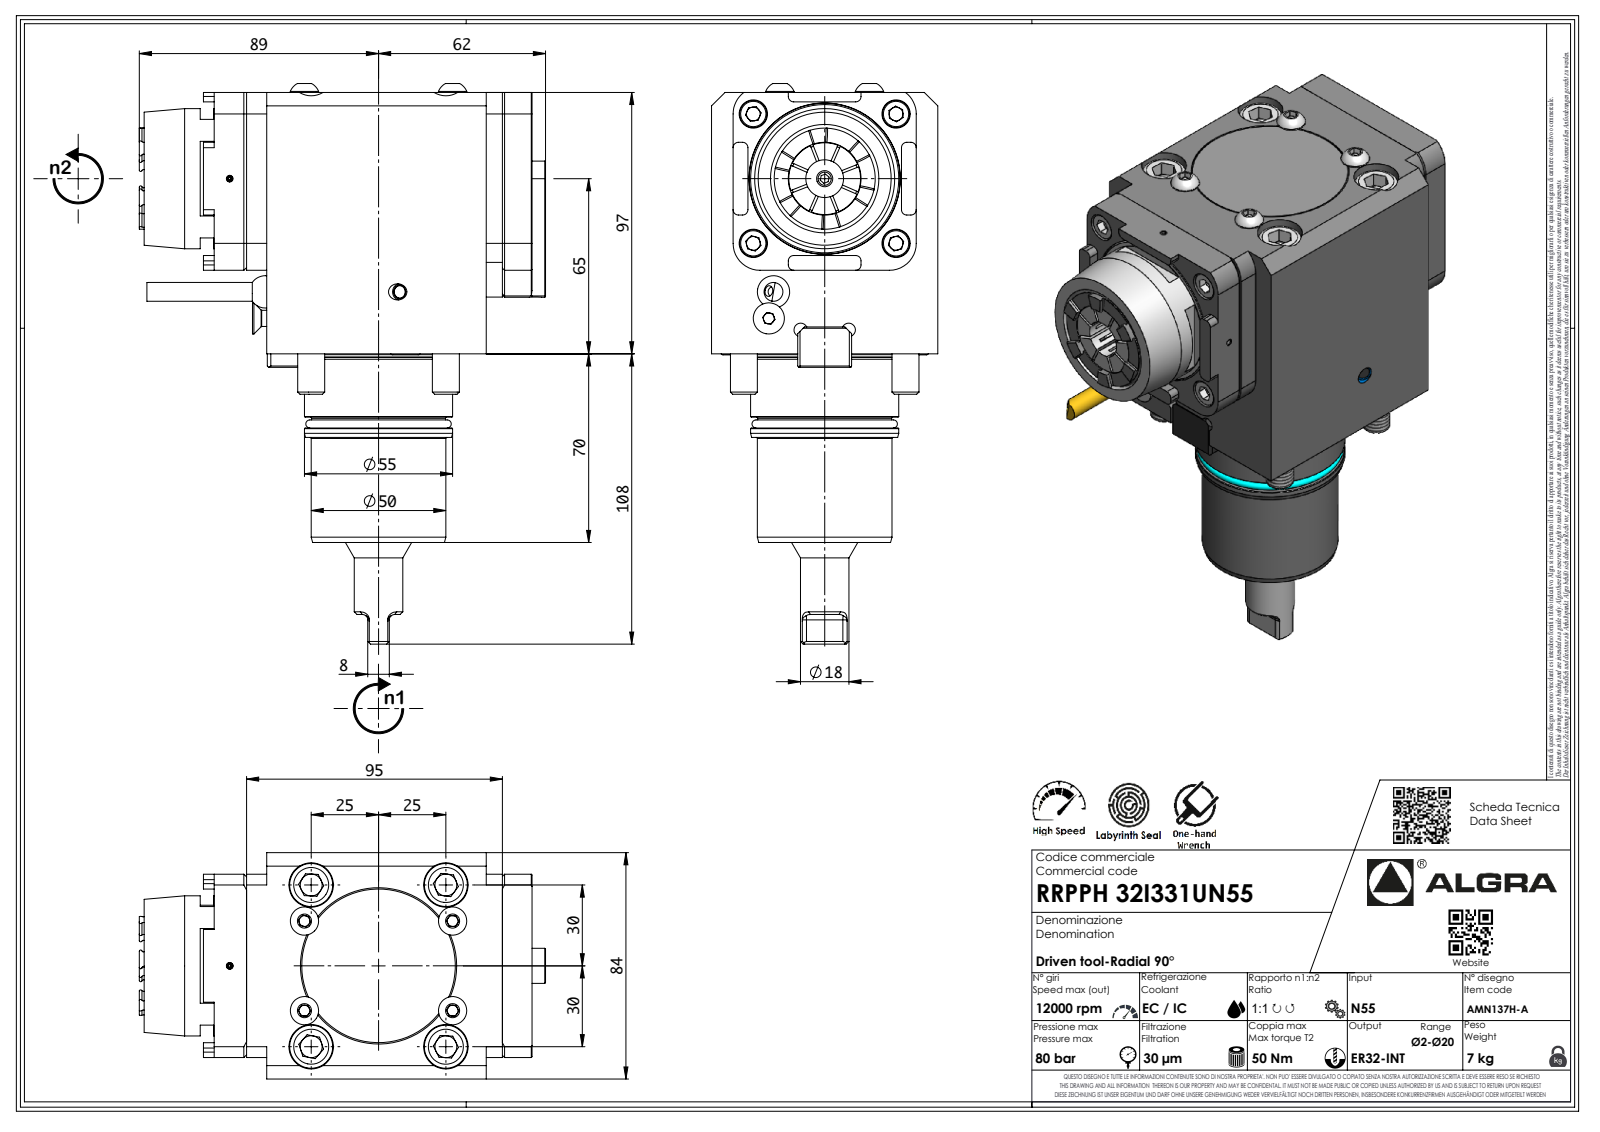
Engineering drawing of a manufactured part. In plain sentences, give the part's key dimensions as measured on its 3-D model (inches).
The part is named "RRPPH32I331UN55". Its 3-D file was written by "SolidWorks 2023 (AUTOMOTIVE_DESIGN)". It is 1 solid with 584 faces: 326 planar, 98 cylindrical and 160 other. Overall it measures 8.059 by 5.721 by 3.307 inches. Its volume is 63.22 cubic inches and its surface area 118.6 square inches. Round holes: 1 of diameter 0.124, 1 of diameter 0.337, 1 of diameter 0.472, 1 of diameter 2.283. Round bosses or shafts: 1 of diameter 2.165, 1 of diameter 2.15, 1 of diameter 2.047, 1 of diameter 1.969, 1 of diameter 1.957, 1 of diameter 0.709, 1 of diameter 0.456, 1 of diameter 0.376. Partial cylindrical surfaces (rounded edges, fillets, slot ends): 20 of radius 0.079, 7 of radius 0.02, 7 of radius 0.031, 7 of radius 0.219, 4 of radius 0.394, 3 of radius 0.098, 1 of radius 0.012, 1 of radius 0.118. The main face-to-face distances are 3.307, 3.819, 0.315, 2.992, 3.858, 0.65, 3.209, 3.976, 3.817, 1.024.
